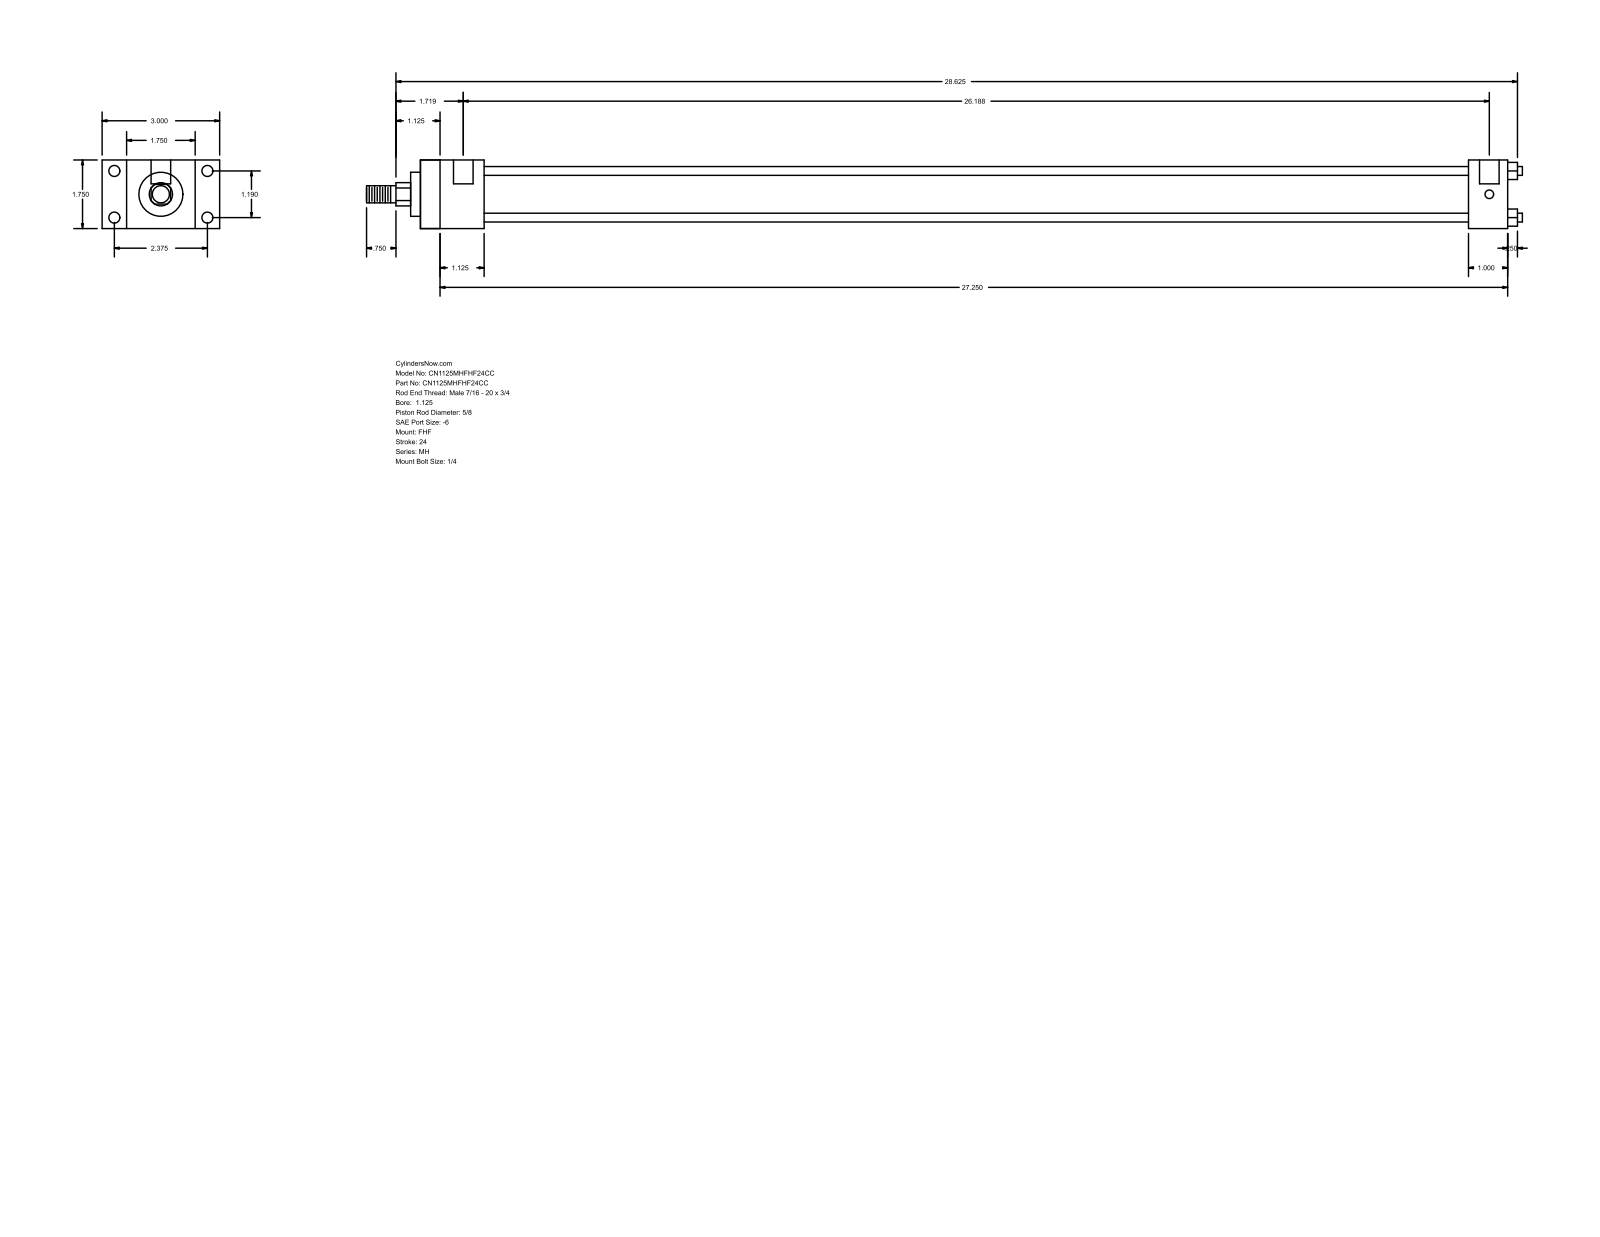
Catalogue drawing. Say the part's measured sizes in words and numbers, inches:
The part is named "MH_FHF__0112_0.625". Its 3-D file was written by "GSSL Pune (CONFIG_CONTROL_DESIGN)". It is 0 solids with 88 faces: 60 planar, 28 cylindrical and 0 other. Overall it measures 29.5 by 3 by 1.75 inches. Round holes: 4 of diameter 0.219, 4 of diameter 0.281, 2 of diameter 0.5. Round bosses or shafts: 4 of diameter 0.225, 1 of diameter 1.375, 1 of diameter 1.125, 1 of diameter 0.625, 1 of diameter 0.437. Partial cylindrical surfaces (rounded edges, fillets, slot ends): 1 of radius 0.297. The main face-to-face distances are 1.75, 0.625, 2.375, 1.625, 3, 27.75, 26.125, 1, 26.75, 25.125. The hole center spacings are 1.19, 2.375, 2.656, 26.063, 0.125, 26.187.
